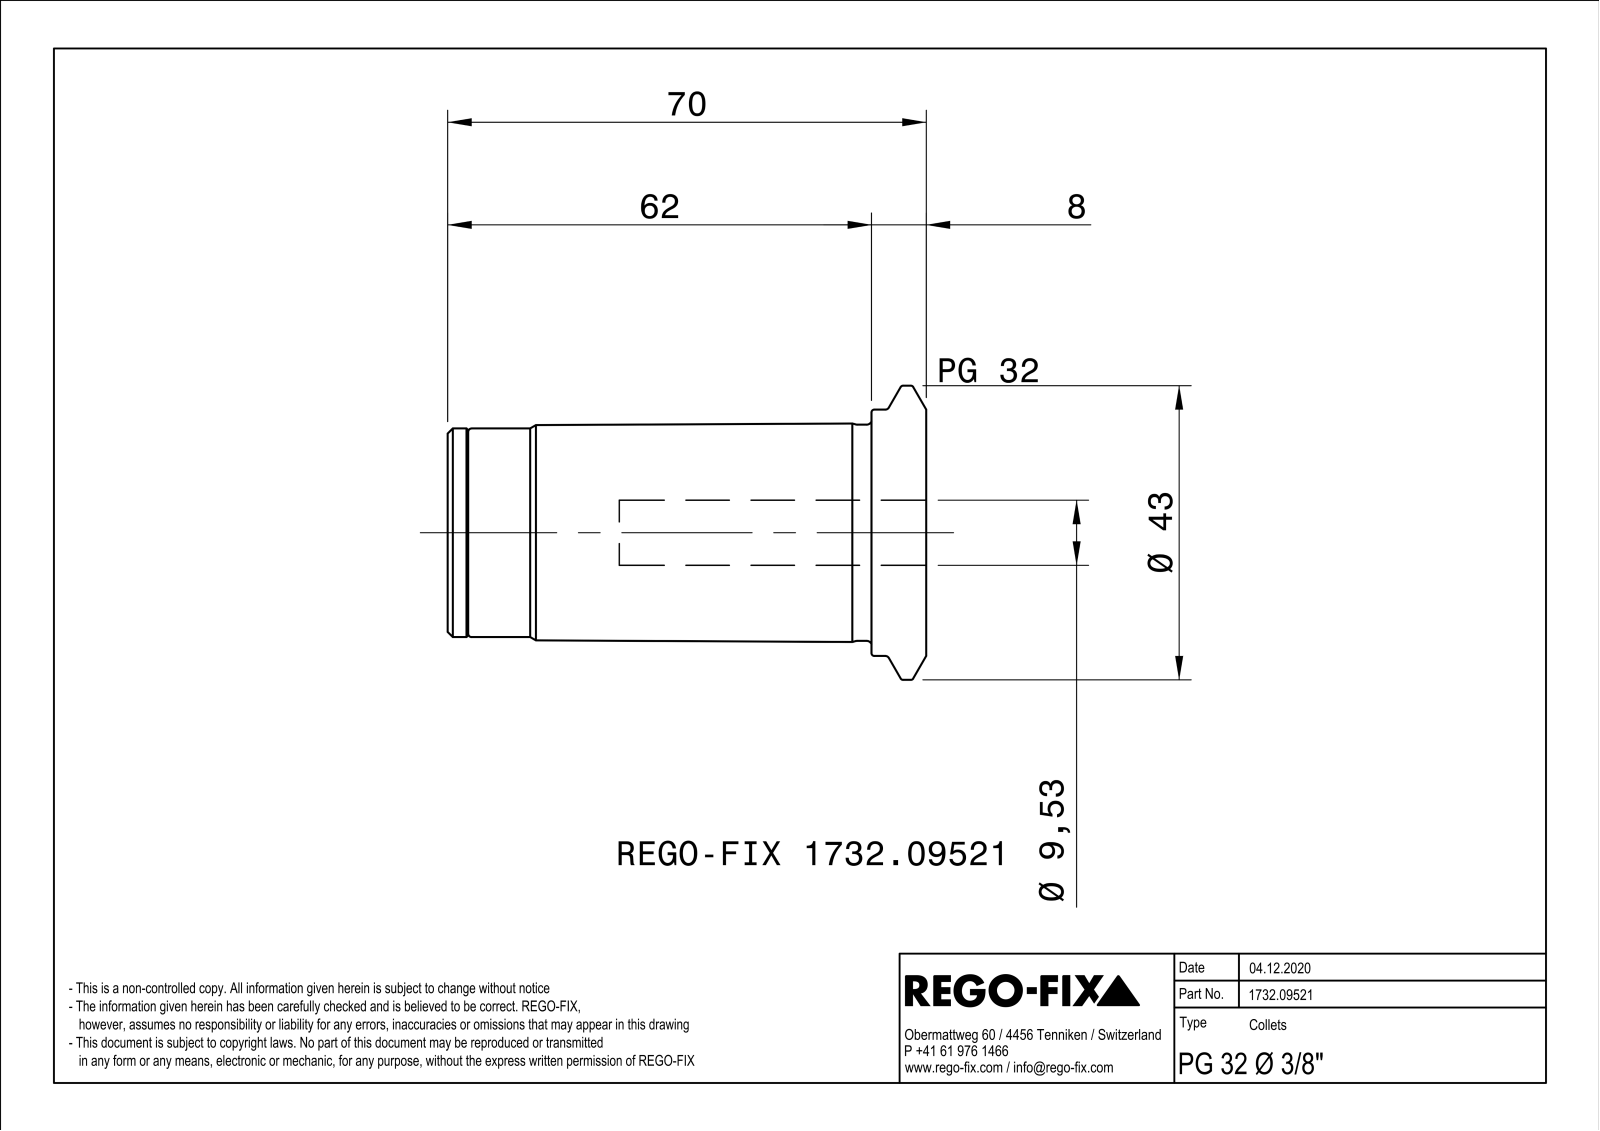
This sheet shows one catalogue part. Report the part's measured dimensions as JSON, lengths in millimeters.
{"part_name": "NOCUT", "step_written_by": "SIEMENS PLM Software Solid Edge ST10 (AUTOMOTIVE_DESIGN)", "units": "millimeters", "bodies": {"solids": 1, "faces": 127, "planar": 31, "cylindrical": 41, "other": 55}, "overall_size": [70, 43, 42.99], "volume_mm3": 46949, "surface_area_mm2": 16614, "round_holes": [[4, 3], [8.92, 1], [9.53, 1], [10.5, 1], [15.5, 1], [26.92, 1], [28.5, 1]], "round_bosses_or_shafts": [[43, 1], [36, 1], [31.6, 1], [30.5, 1], [26.5, 1], [21, 1]], "partial_cylinders_radius": [[2, 6], [3.5, 3], [3.98, 1], [4.75, 1], [8.75, 1]], "face_to_face_distances": [1, 70, 58, 12, 59, 11, 8, 60, 2, 10], "hole_center_spacings": [7.75, 13.42, 13.43]}
